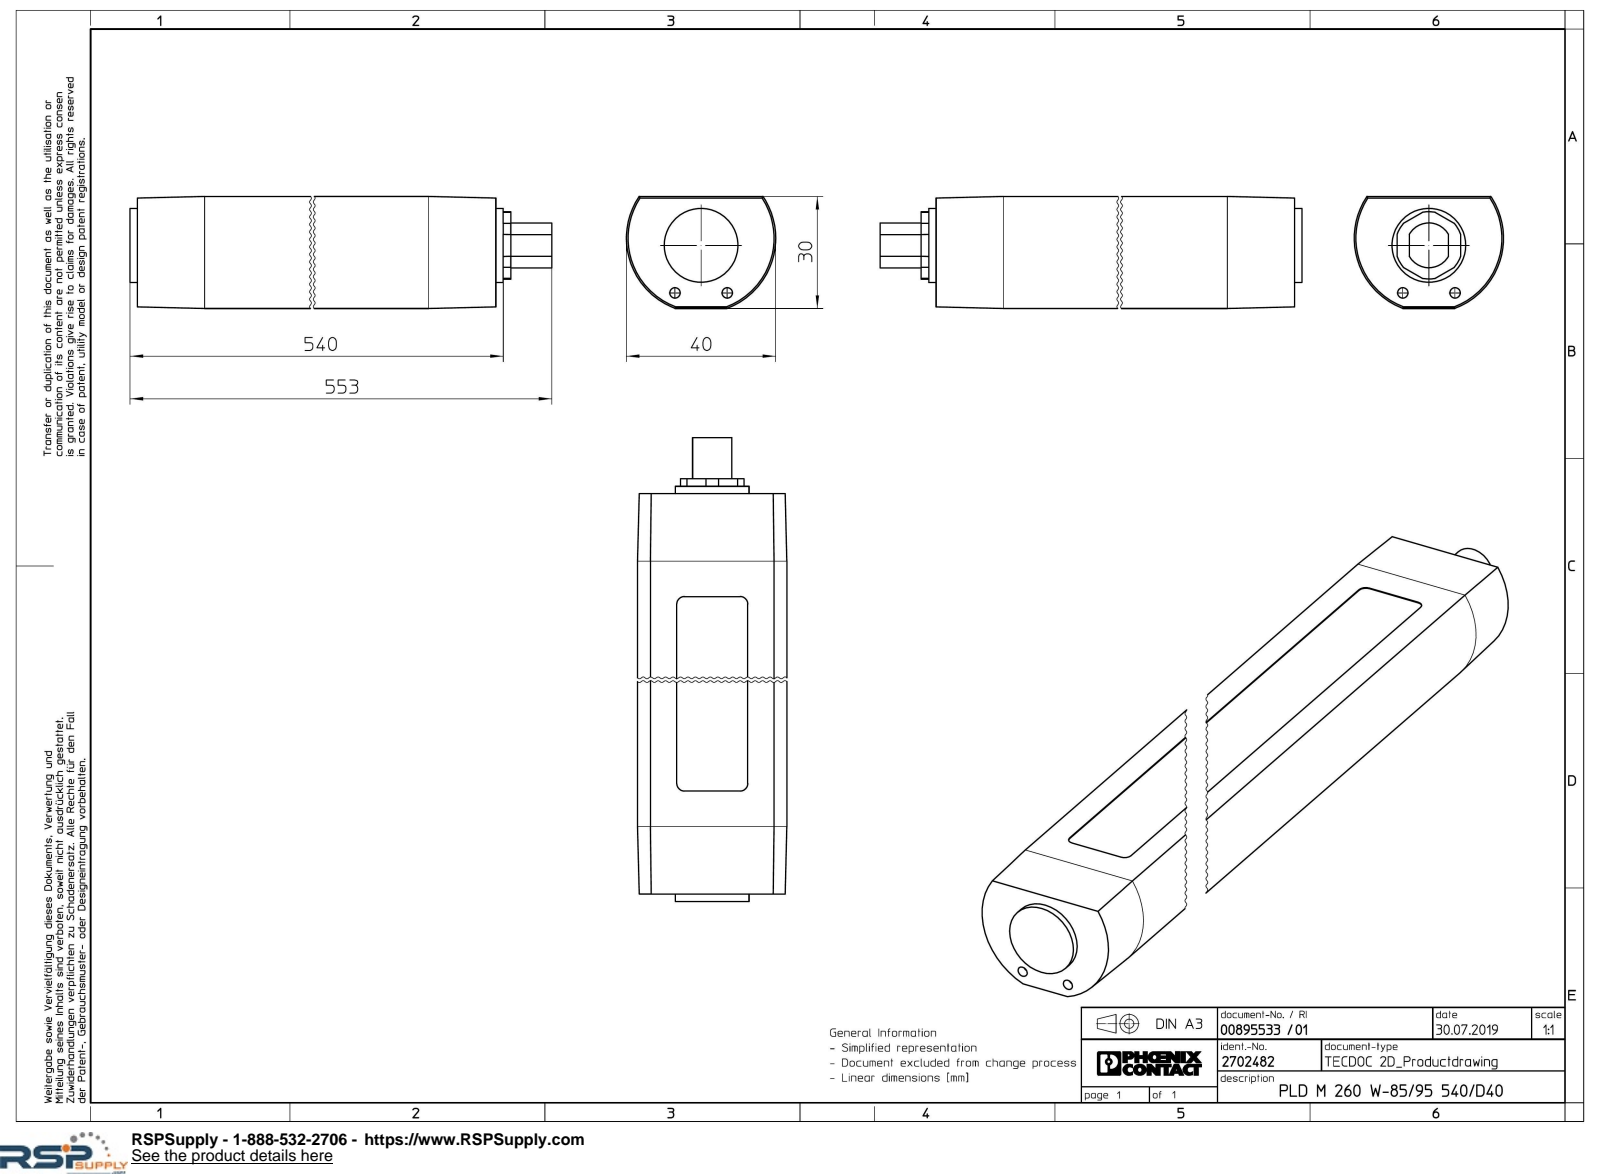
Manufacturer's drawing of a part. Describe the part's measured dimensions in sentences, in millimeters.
The part is named "PLD_M_260_W_75_95_540_D40-select". Its 3-D file was written by "Creo Elements/Direct Modeling 20.1A 29-Sep-2018 (C) Parametric Technology GmbH (AUTOMOTIVE_DESIGN)". It is 1 solid with 59 faces: 29 planar, 26 cylindrical and 4 other. Overall it measures 553 by 40 by 29.95 millimeters. Its volume is 557 480 cubic millimeters and its surface area 67 025 square millimeters. Round holes: 2 of diameter 2.8. Round bosses or shafts: 1 of diameter 19.75. Partial cylindrical surfaces (rounded edges, fillets, slot ends): 4 of radius 2, 1 of radius 6, 1 of radius 9, 1 of radius 20. The main face-to-face distances are 29.75, 29.95, 536, 41.95, 2, 538, 540, 4, 542, 4.25. The hole center spacings are 14.
